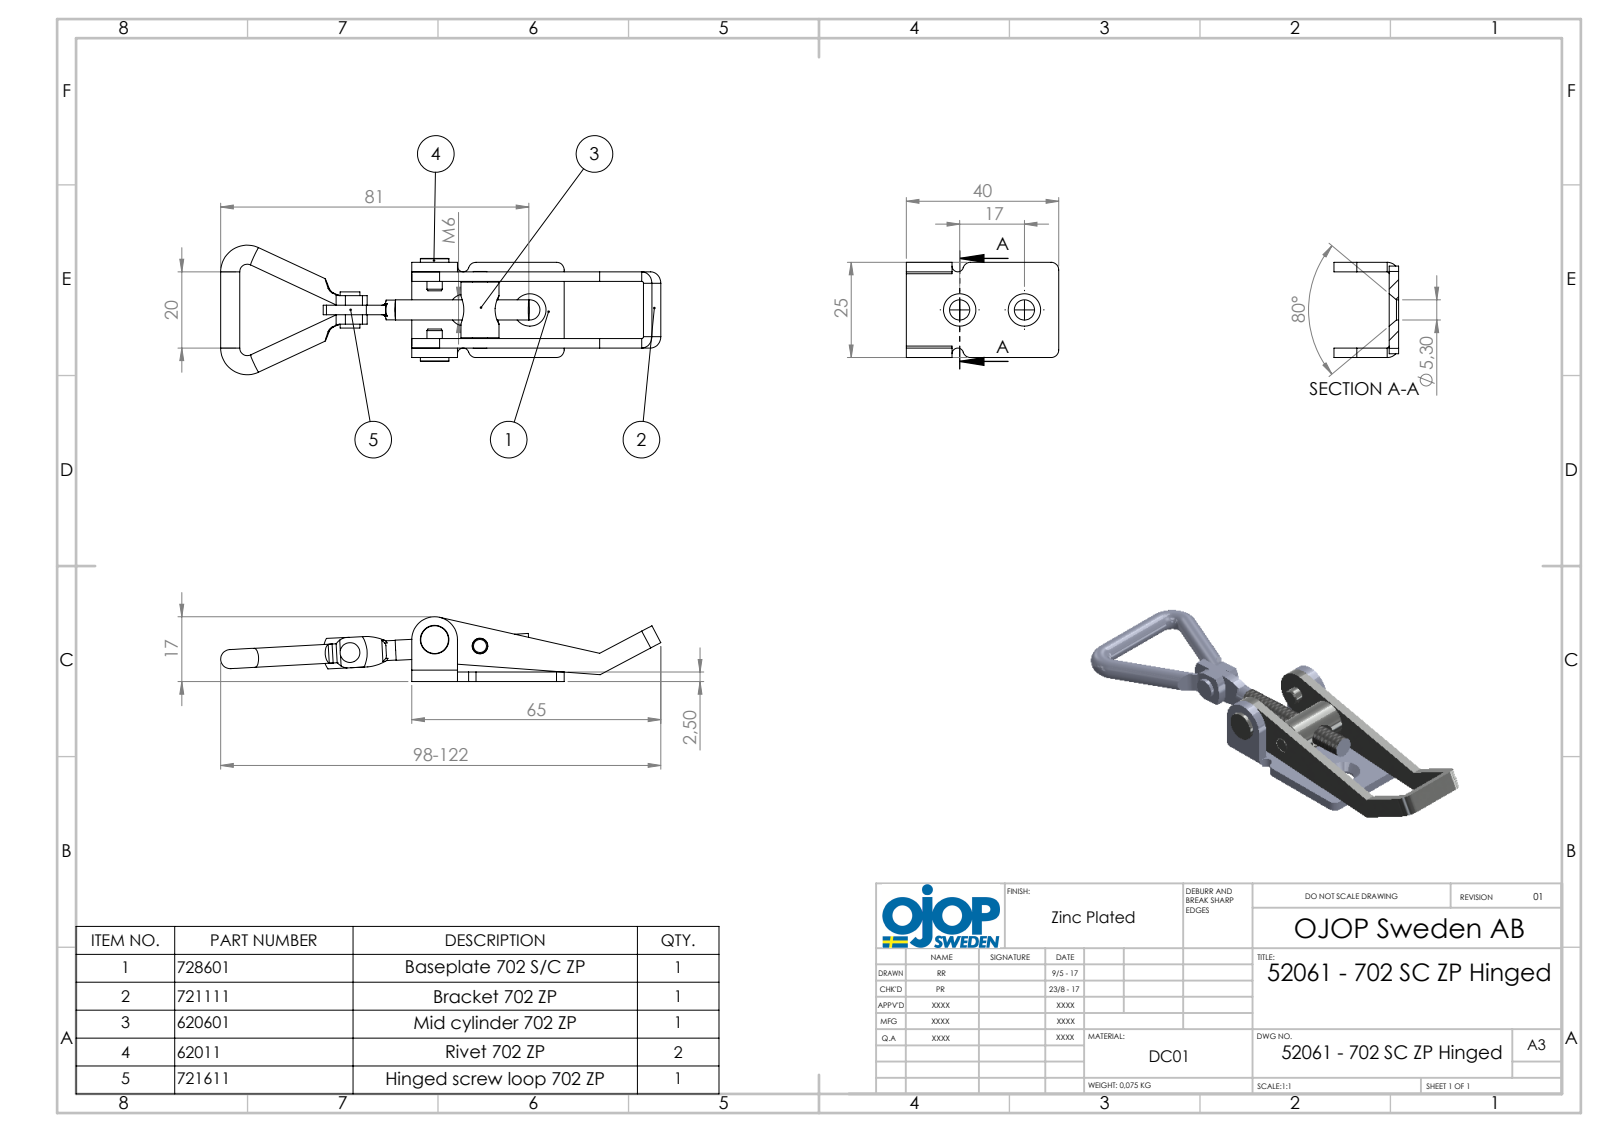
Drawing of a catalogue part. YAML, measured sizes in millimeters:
part_name: "702 - Nit till ledad M6; 702 - Ring till ledad M6; 702 - Skruv till ledad M6; 702 - Ansatsnit (+5 more)"
step_written_by: "SolidWorks 2015 (AUTOMOTIVE_DESIGN)"
units: millimeters
bodies: {solids: 8, faces: 207, planar: 80, cylindrical: 101, other: 26}
overall_size: [115.53, 34, 17]
volume: 10043
surface_area: 10133
round_holes:
  - {diameter: 4.1, count: 3}
  - {diameter: 5.3, count: 2}
  - {diameter: 5, count: 1}
  - {diameter: 6, count: 1}
round_bosses_or_shafts:
  - {diameter: 5, count: 3}
  - {diameter: 4, count: 2}
  - {diameter: 10, count: 1}
  - {diameter: 7.5, count: 1}
  - {diameter: 5.3, count: 1}
  - {diameter: 5.2, count: 1}
  - {diameter: 5.18, count: 1}
partial_cylinders:
  - {radius: 2, count: 8}
  - {radius: 1, count: 6}
  - {radius: 0.5, count: 4}
  - {radius: 3, count: 4}
  - {radius: 1.5, count: 2}
  - {radius: 6.78, count: 2}
  - {radius: 12.31, count: 2}
  - {radius: 3.85, count: 1}
face_to_face_distances: [2.5, 20, 17.5, 8.75, 11.25, 5, 15, 6.25, 13.75, 22.5]
hole_center_spacings: [12.03, 17, 22.47, 34.16]
